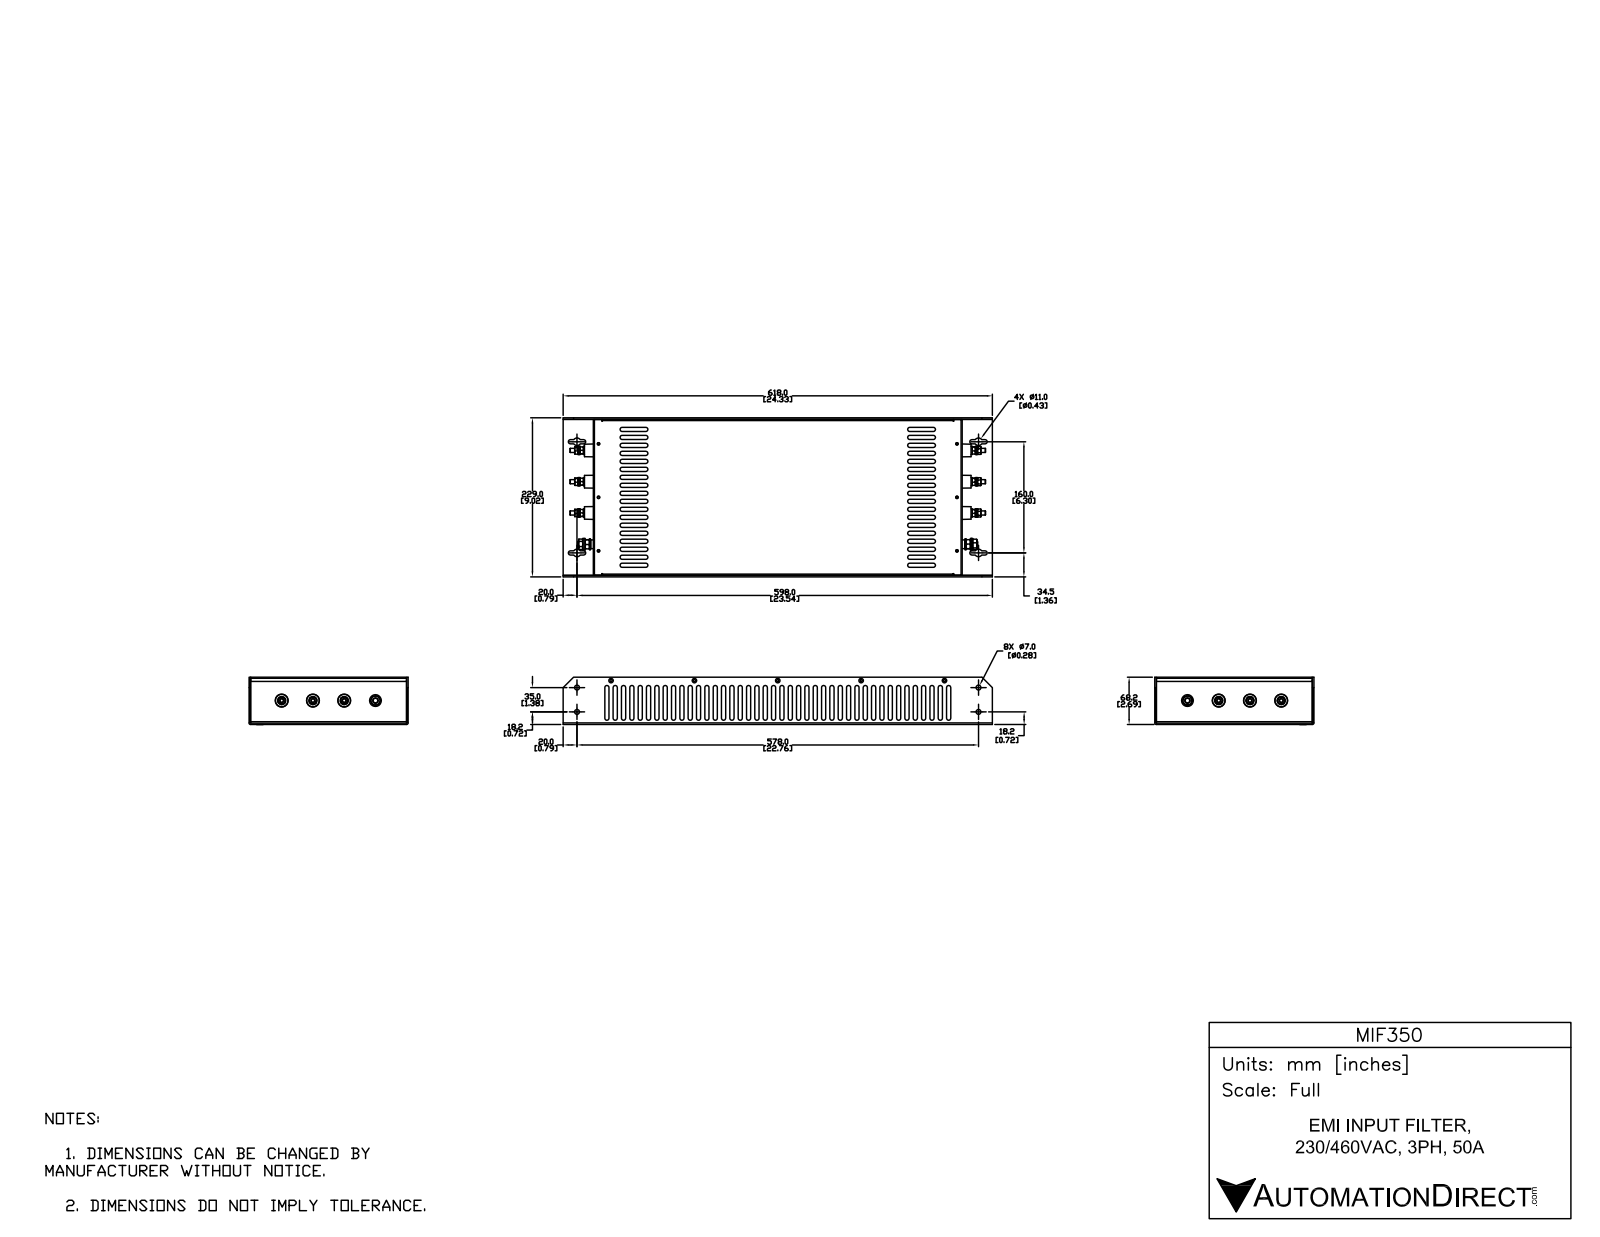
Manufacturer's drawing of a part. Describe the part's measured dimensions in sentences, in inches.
The part is named "MIF350-350B r1". Its 3-D file was written by "SolidWorks 2017 (AUTOMOTIVE_DESIGN)". It is 59 solids with 2513 faces: 780 planar, 874 cylindrical and 859 other. Overall it measures 24.331 by 9.016 by 2.685 inches. Its volume is 38.64 cubic inches and its surface area 1 238 square inches. Round holes: 11 of diameter 0.13, 11 of diameter 0.197, 6 of diameter 0.138, 4 of diameter 0.276, 3 of diameter 0.236, 3 of diameter 0.256, 3 of diameter 0.354, 3 of diameter 0.362, 1 of diameter 0.268, 1 of diameter 0.335. Round bosses or shafts: 3 of diameter 0.465, 1 of diameter 0.663, 1 of diameter 0.622, 1 of diameter 0.512, 1 of diameter 0.498, 1 of diameter 0.412, 1 of diameter 0.387, 1 of diameter 0.315. Partial cylindrical surfaces (rounded edges, fillets, slot ends): 168 of radius 0.118, 8 of radius 0.031, 8 of radius 0.079, 8 of radius 0.128, 6 of radius 0.016, 4 of radius 0.063, 4 of radius 0.217, 2 of radius 0.094. The main face-to-face distances are 0.079, 0.047, 2.559, 2.638, 2.685, 2.606, 8.937, 8.858, 9.016, 20.756. The hole center spacings are 0.492, 3.031, 3.438, 4.724, 6.463, 20.024, 20.311, 20.54.
